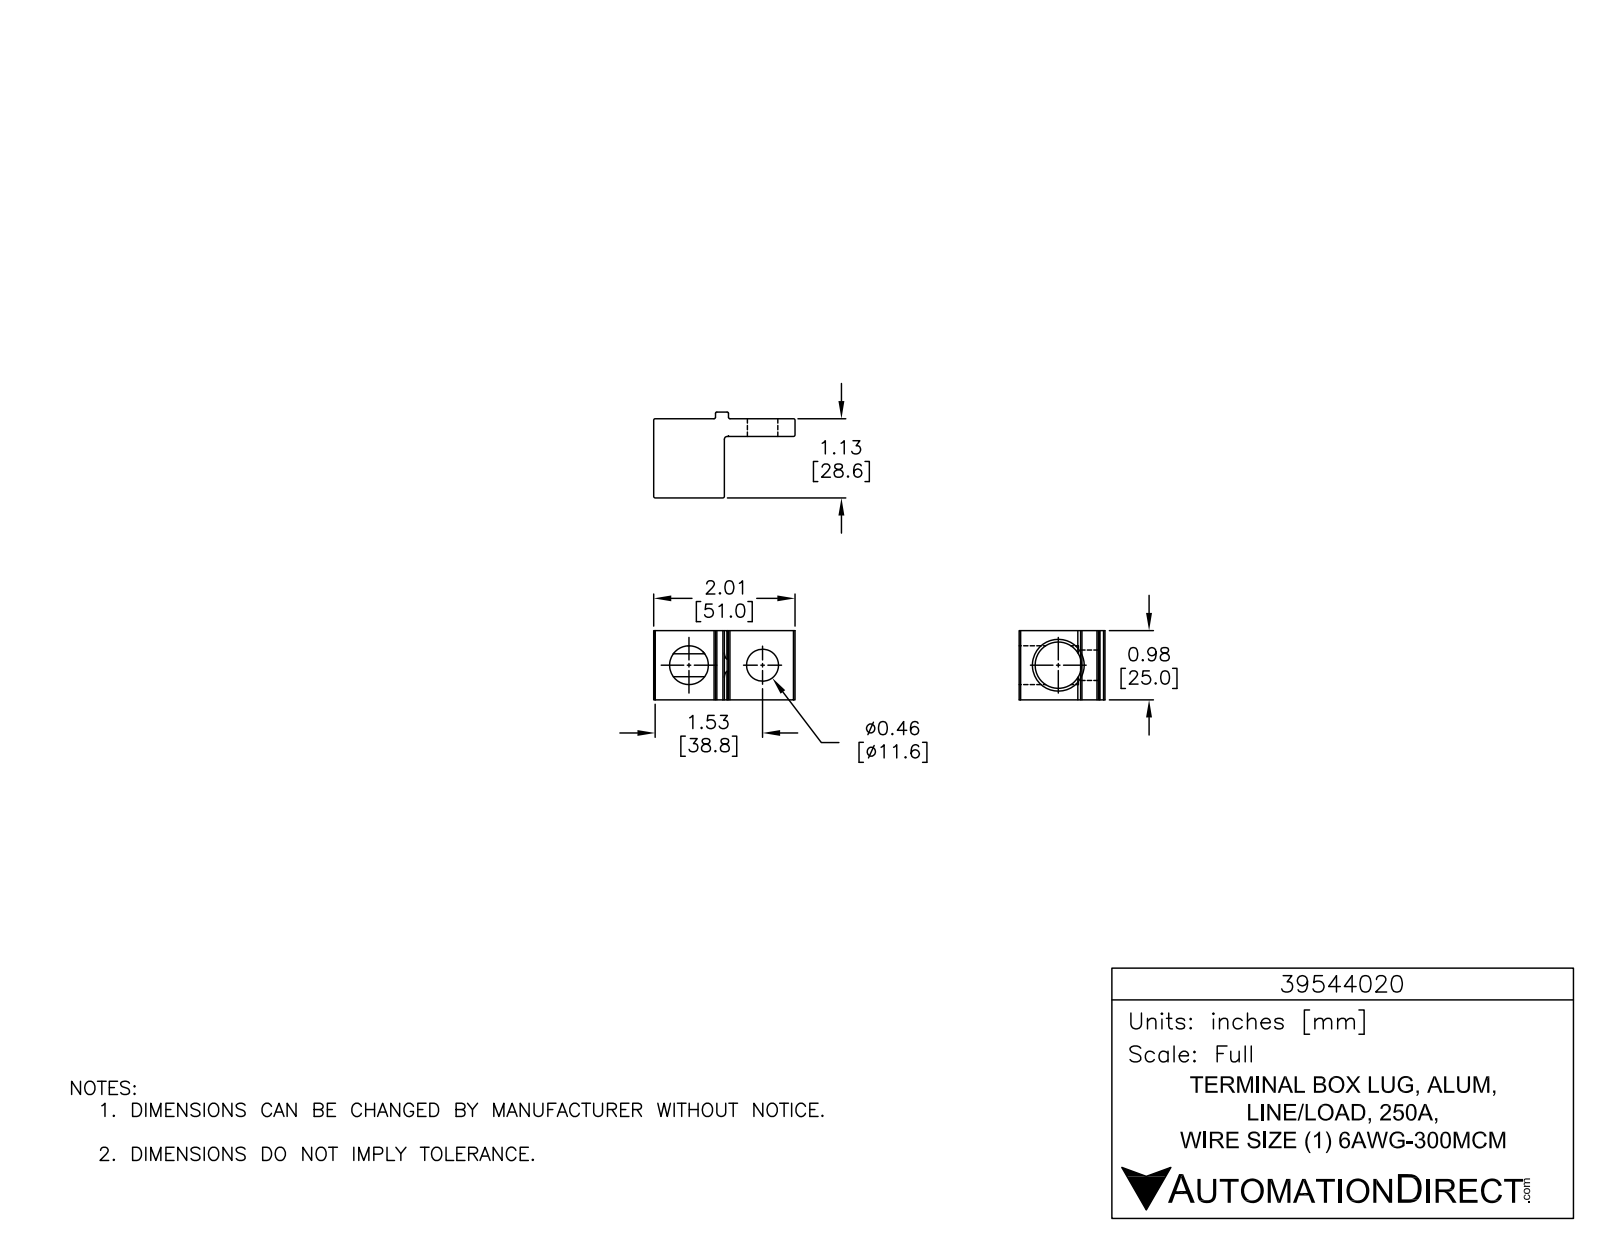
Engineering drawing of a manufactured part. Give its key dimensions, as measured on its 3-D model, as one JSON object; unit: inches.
{"part_name": "39544020", "step_written_by": "SolidWorks 2015 (AUTOMOTIVE_DESIGN)", "units": "inches", "bodies": {"solids": 1, "faces": 37, "planar": 15, "cylindrical": 20, "other": 2}, "overall_size": [2.008, 1.22, 0.984], "volume_in3": 0.934, "surface_area_in2": 10.52, "round_holes": [[0.433, 1], [0.551, 1], [0.657, 1]], "partial_cylinders_radius": [[0.02, 9], [0.039, 1]], "face_to_face_distances": [0.984, 0.252, 1.126, 0.874, 1.004, 2.008, 0.094, 0.346, 1.22, 0.378], "hole_center_spacings": [1.045]}
